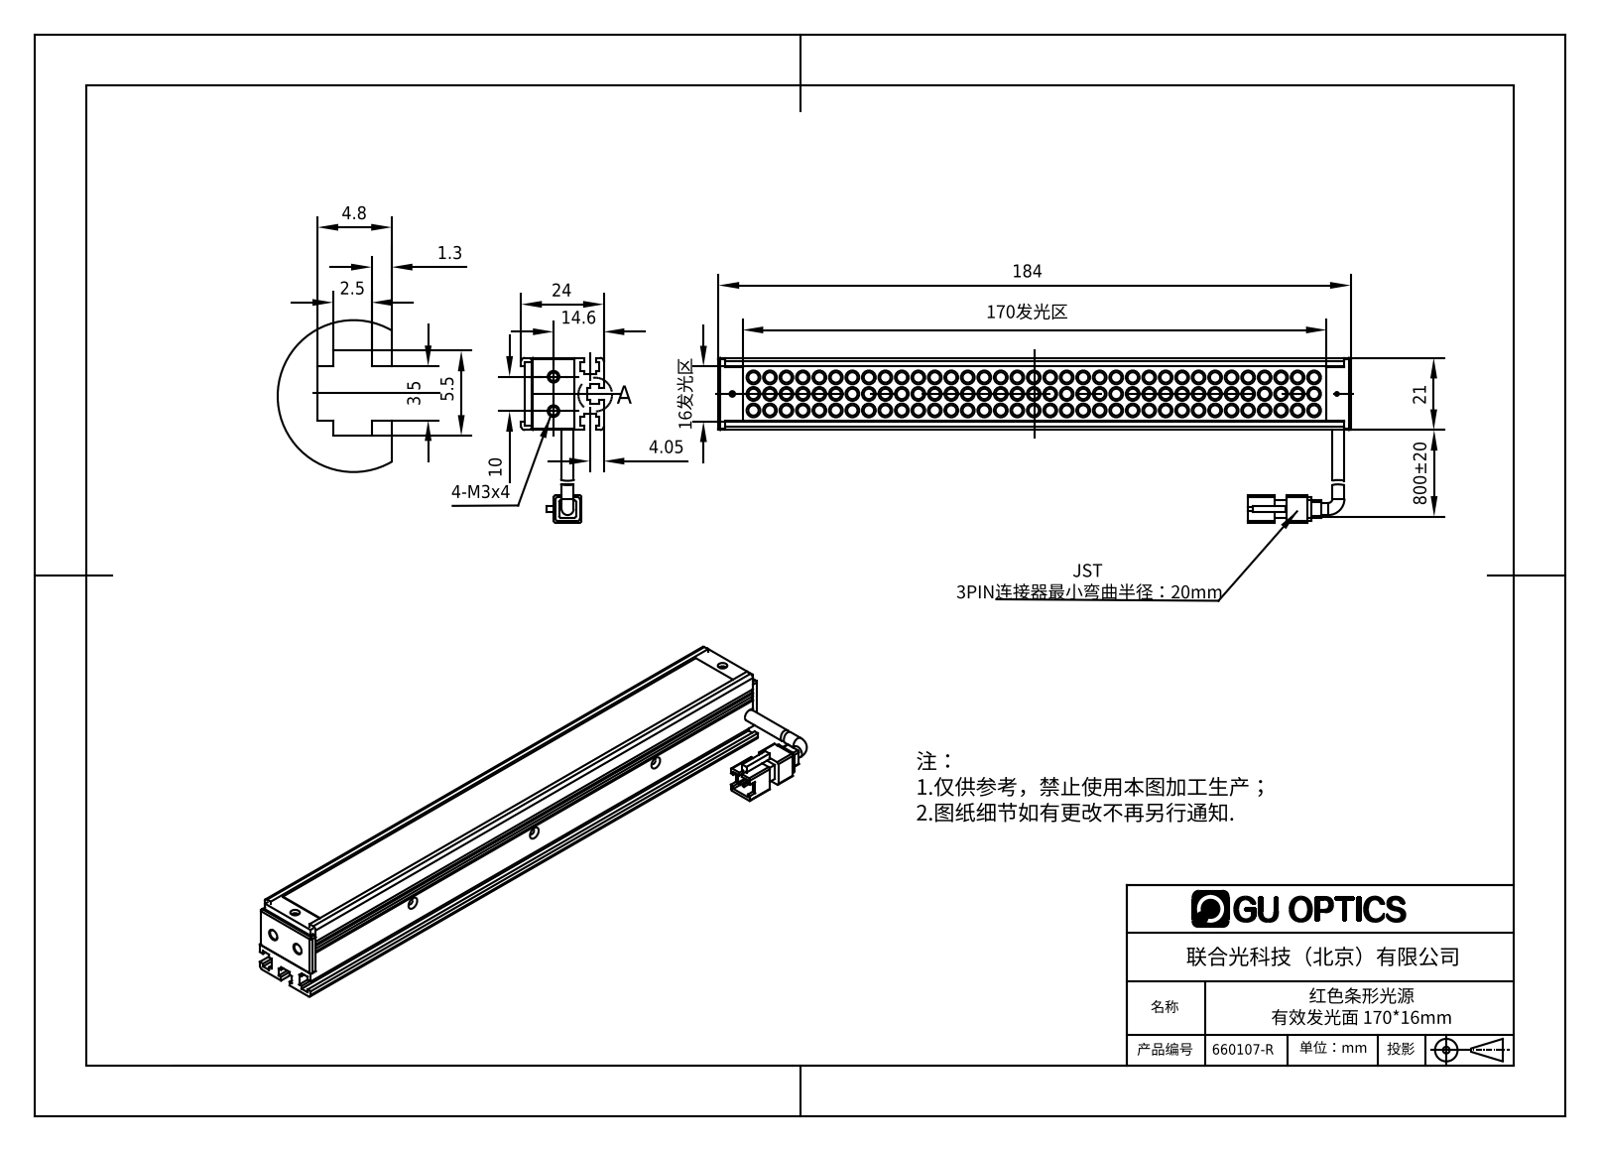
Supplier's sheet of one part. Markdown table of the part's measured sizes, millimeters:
| quantity | value |
| --- | --- |
| part name | 660107-R |
| STEP written by | SolidWorks 2016 (AUTOMOTIVE_DESIGN) |
| units | millimeters |
| bodies | 8 solids, 1075 faces (356 planar, 507 cylindrical, 212 other) |
| overall size | 184 × 48 × 24 |
| volume | 53 223 mm³ |
| surface area | 59 208 mm² |
| round holes (diameter × count) | 1.6 × 5, 1.7 × 3, 1.5 × 2, 2.5 × 2, 2.8 × 2, 3 × 2, 1.1 × 1, 1.25 × 1, 2 × 1 |
| round bosses / shafts (diameter × count) | 4 × 105, 3 × 105, 3.5 × 2 |
| partial cylindrical surfaces (radius × count) | 1 × 12, 0.5 × 8, 1.65 × 1 |
| main face-to-face distances | 1, 2.5, 2, 18.5, 21, 4, 14.6, 1.3, 2.2, 3.5 |
| hole center spacings | 176, 7, 38.03, 38.38, 50, 88.01, 88.17, 138.01 |
